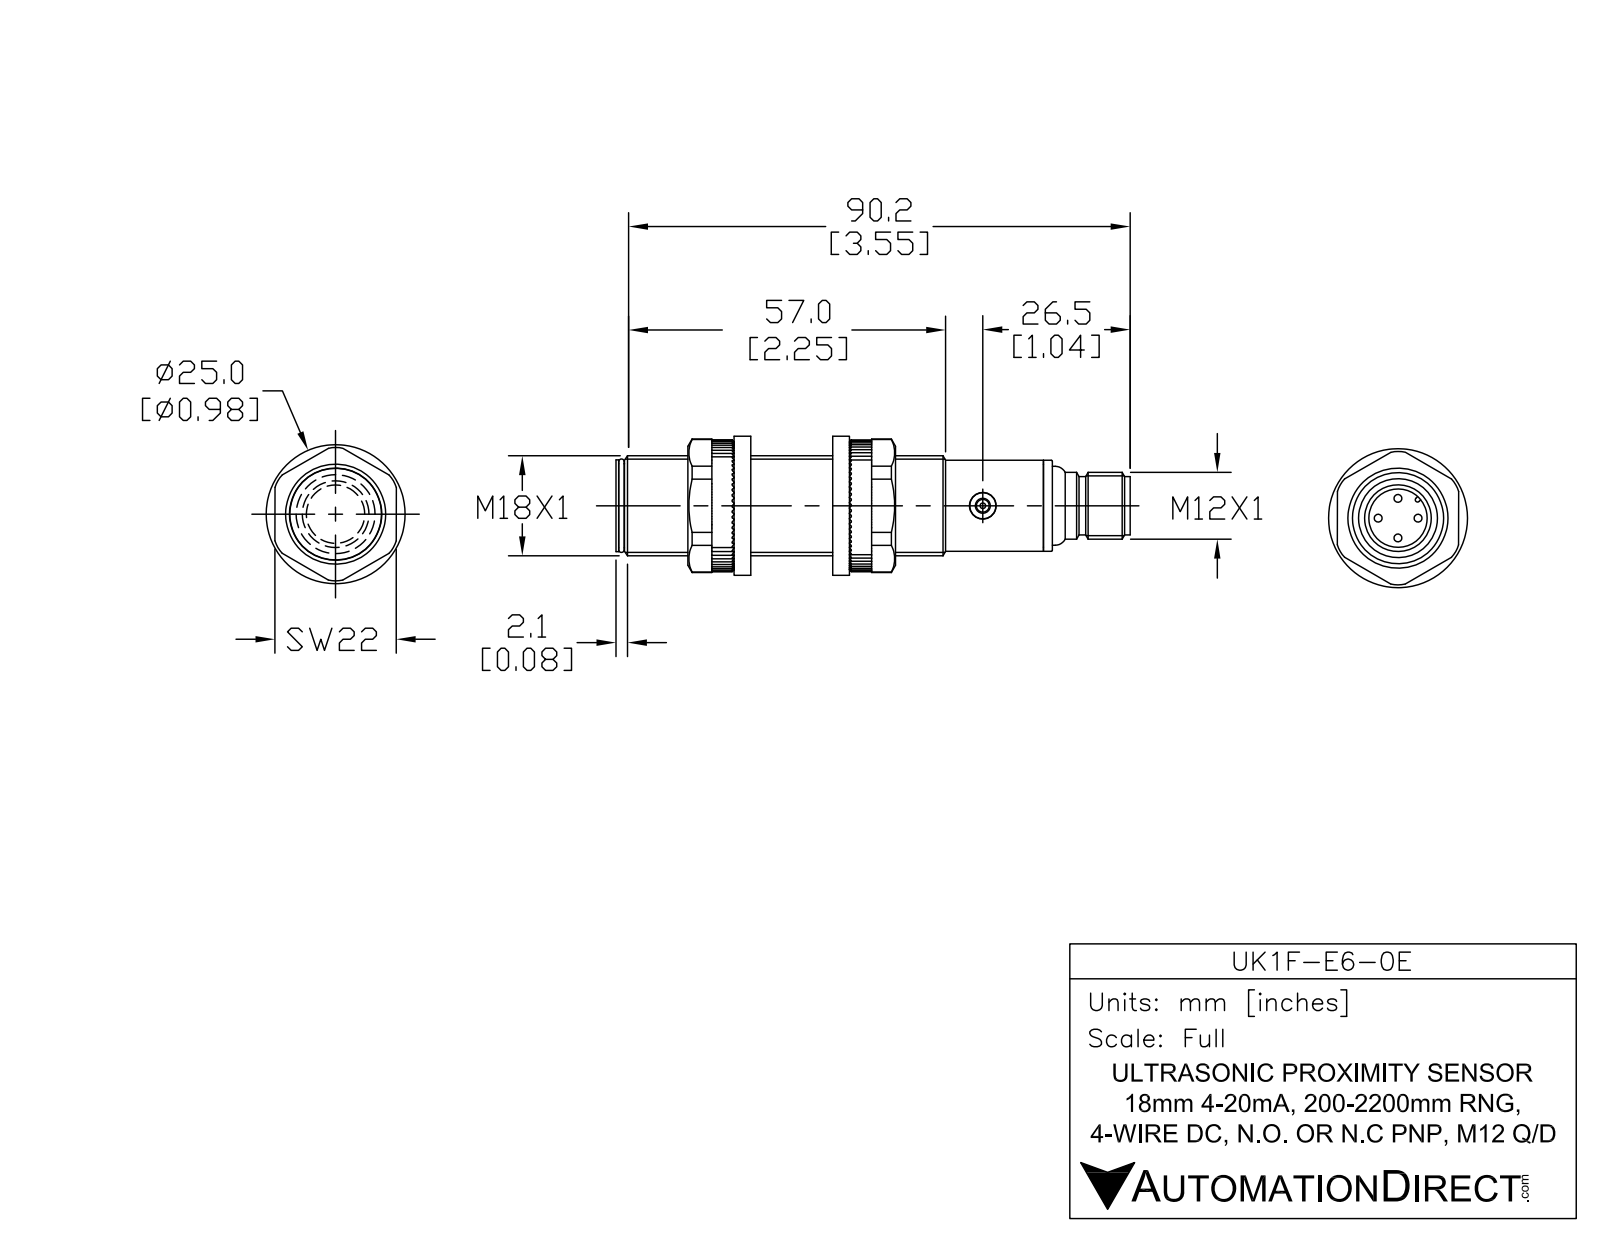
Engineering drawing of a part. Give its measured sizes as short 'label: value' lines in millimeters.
name: UK1F-E6-0E
written by: SolidWorks 2017 (AUTOMOTIVE_DESIGN)
unit: mm
bodies: 6 solids, 106 faces (21 planar, 48 cylindrical, 37 other)
size: 91.6 × 18 × 18
volume: 19 700 mm³; area: 6 890 mm²
holes: 1× ⌀2.7, 1× ⌀4.7, 1× ⌀7, 1× ⌀8.3, 1× ⌀9.5
bosses: 4× ⌀1, 1× ⌀18, 1× ⌀16.6, 1× ⌀16.4, 1× ⌀15.8, 1× ⌀14.2, 1× ⌀12, 1× ⌀10.5
rounds: 1× R0.6
face distances: 75.1, 1, 76.1, 0.9, 76, 1.1, 4, 77.6, 77.5, 76.6
